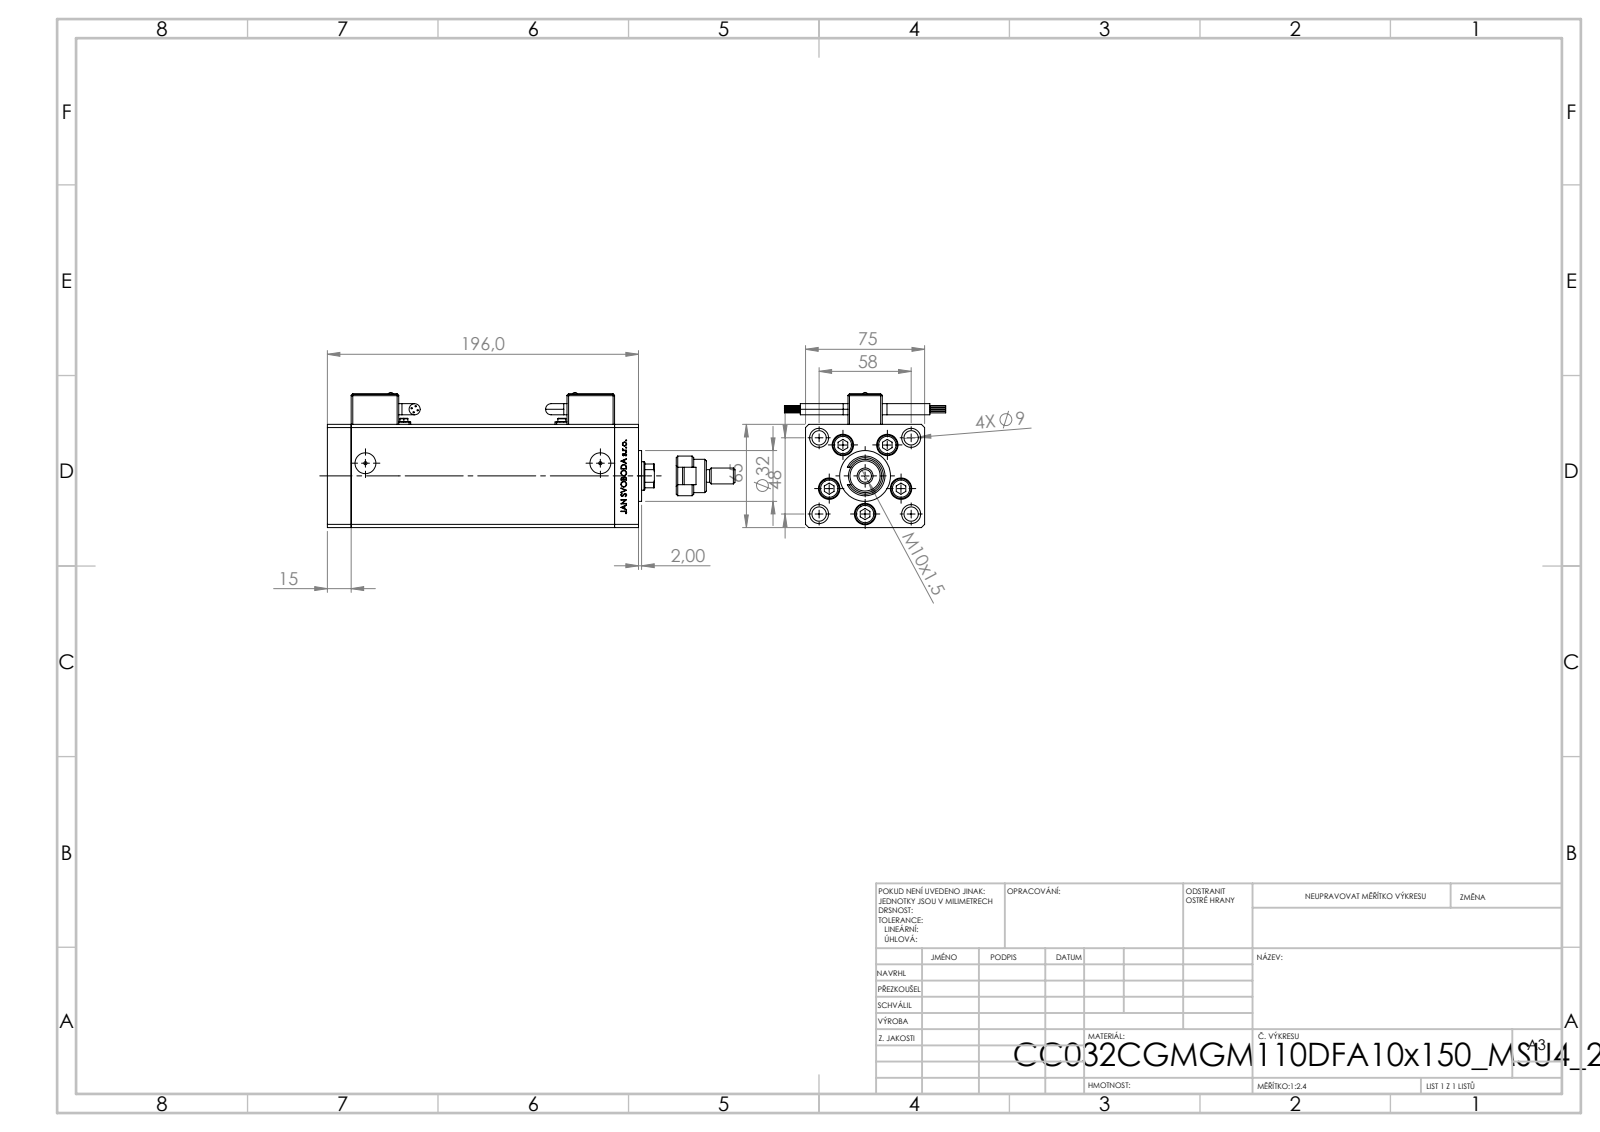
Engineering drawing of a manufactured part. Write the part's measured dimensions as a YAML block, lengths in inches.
part_name: "V220C_C MIDDLE; V220C BACK_C; V220C_VC_C; FEMALE_PART_FOR_DFA (+3 more)"
step_written_by: "SolidWorks 2019 (CONFIG_CONTROL_DESIGN)"
units: inches
bodies: {solids: 15, faces: 1410, planar: 634, cylindrical: 266, other: 510}
overall_size: [10.11, 4, 3.35]
volume: 47.36
surface_area: 270.6
round_holes:
  - {diameter: 0.354, count: 9}
  - {diameter: 0.531, count: 5}
  - {diameter: 0.315, count: 4}
  - {diameter: 0.472, count: 4}
  - {diameter: 0.079, count: 2}
  - {diameter: 0.142, count: 2}
  - {diameter: 0.197, count: 2}
  - {diameter: 0.276, count: 2}
  - {diameter: 0.518, count: 2}
  - {diameter: 0.335, count: 1}
  - {diameter: 0.492, count: 1}
  - {diameter: 0.709, count: 1}
round_bosses_or_shafts:
  - {diameter: 0.033, count: 8}
  - {diameter: 0.315, count: 6}
  - {diameter: 0.492, count: 4}
  - {diameter: 0.276, count: 4}
  - {diameter: 0.236, count: 2}
  - {diameter: 0.138, count: 2}
  - {diameter: 0.098, count: 2}
  - {diameter: 1.26, count: 1}
partial_cylinders:
  - {radius: 0.039, count: 24}
  - {radius: 0.157, count: 4}
  - {radius: 0.037, count: 2}
  - {radius: 0.217, count: 1}
  - {radius: 0.335, count: 1}
  - {radius: 0.344, count: 1}
face_to_face_distances: [2.953, 2.559, 6.535, 0.591, 7.126, 0.256, 7.717, 2.303, 1.902, 1.051]
hole_center_spacings: [0.945, 1.482, 0.325, 0.617, 0.678, 1.091, 1.135, 1.142]
